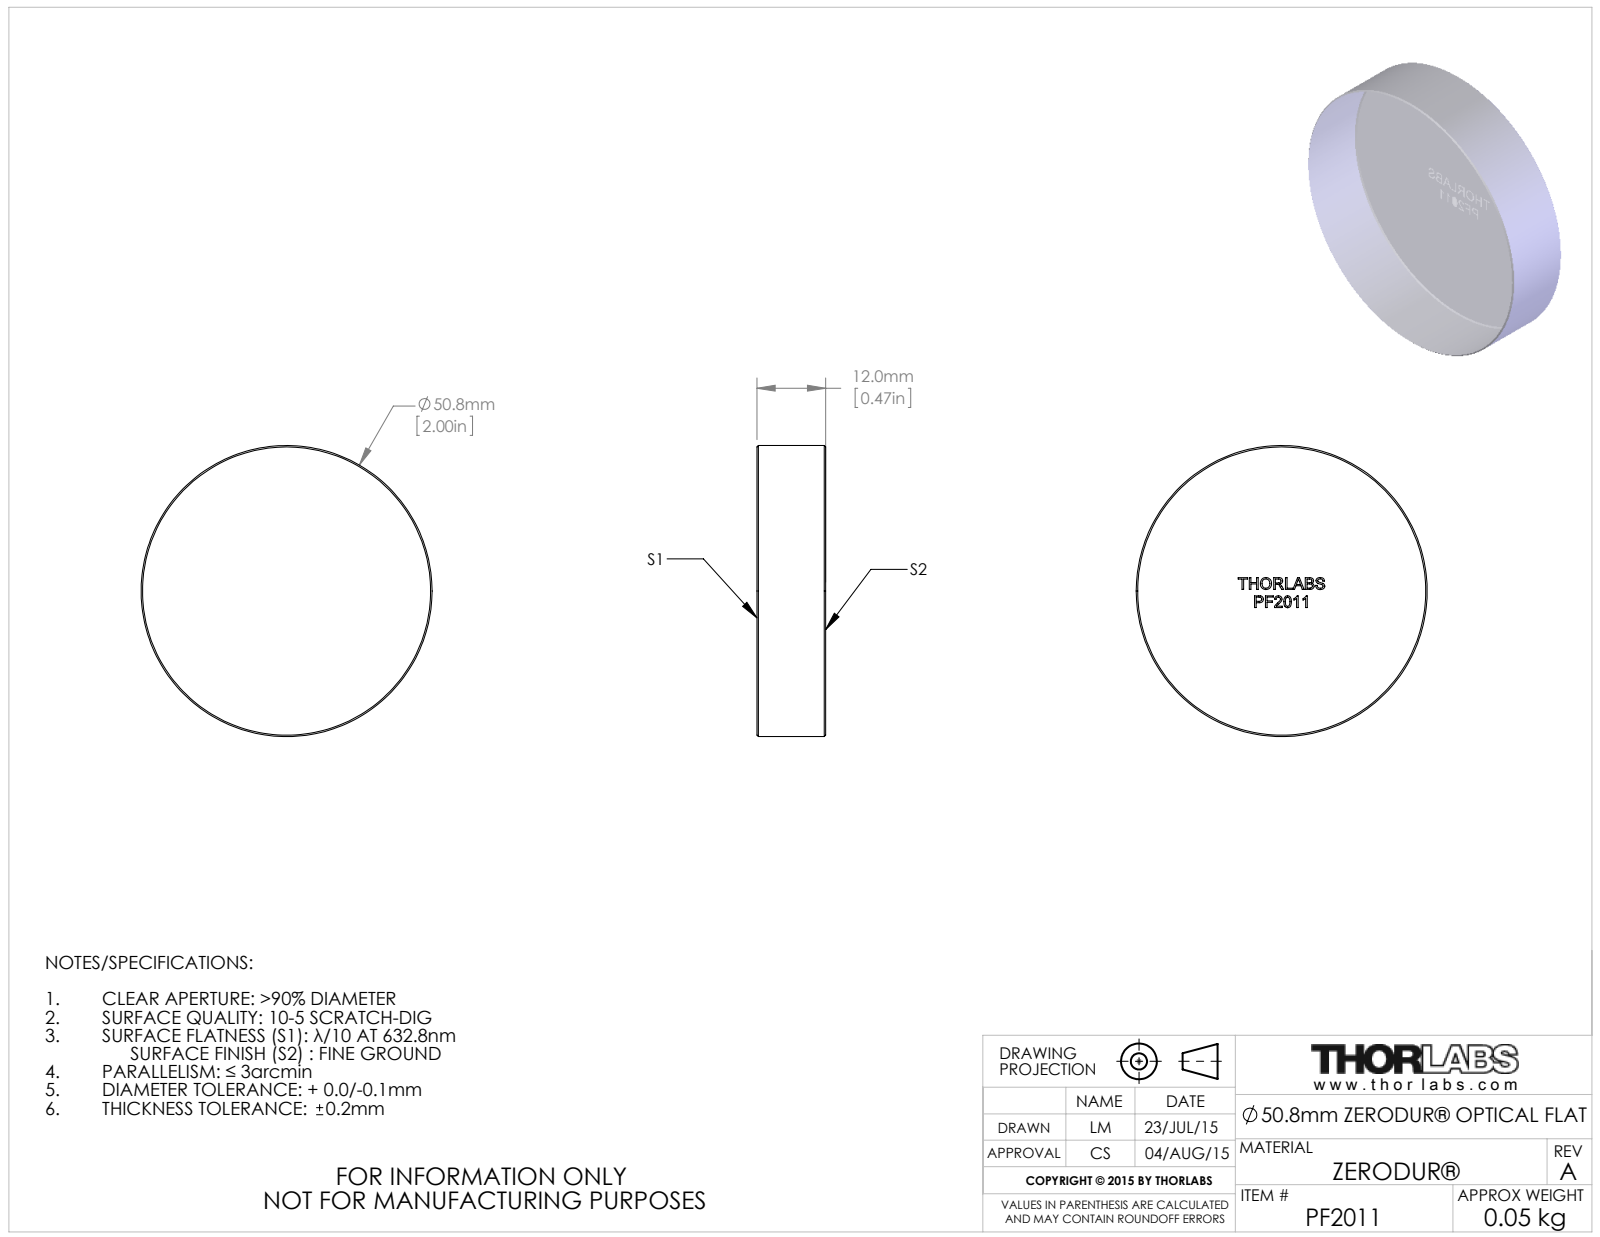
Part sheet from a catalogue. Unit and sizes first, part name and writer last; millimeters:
Units: millimetres
Overall size (bounding box): 50.8 × 50.8 × 12
Round bosses / shafts (diameter × count): ⌀50.8 ×1
Main face-to-face distances: 12, 1.58, 3.16, 5.53, 2.05, 2.55, 1.26, 0.97, 8.55, 2.06
Volume: 24 312 mm³ · Surface area: 5 922 mm²
Bodies: 1 solid, 191 faces (114 planar, 2 cylindrical, 75 other)
Part name (STEP PRODUCT): TTN045230-E0W
STEP written by: SolidWorks 2014 (CONFIG_CONTROL_DESIGN)
